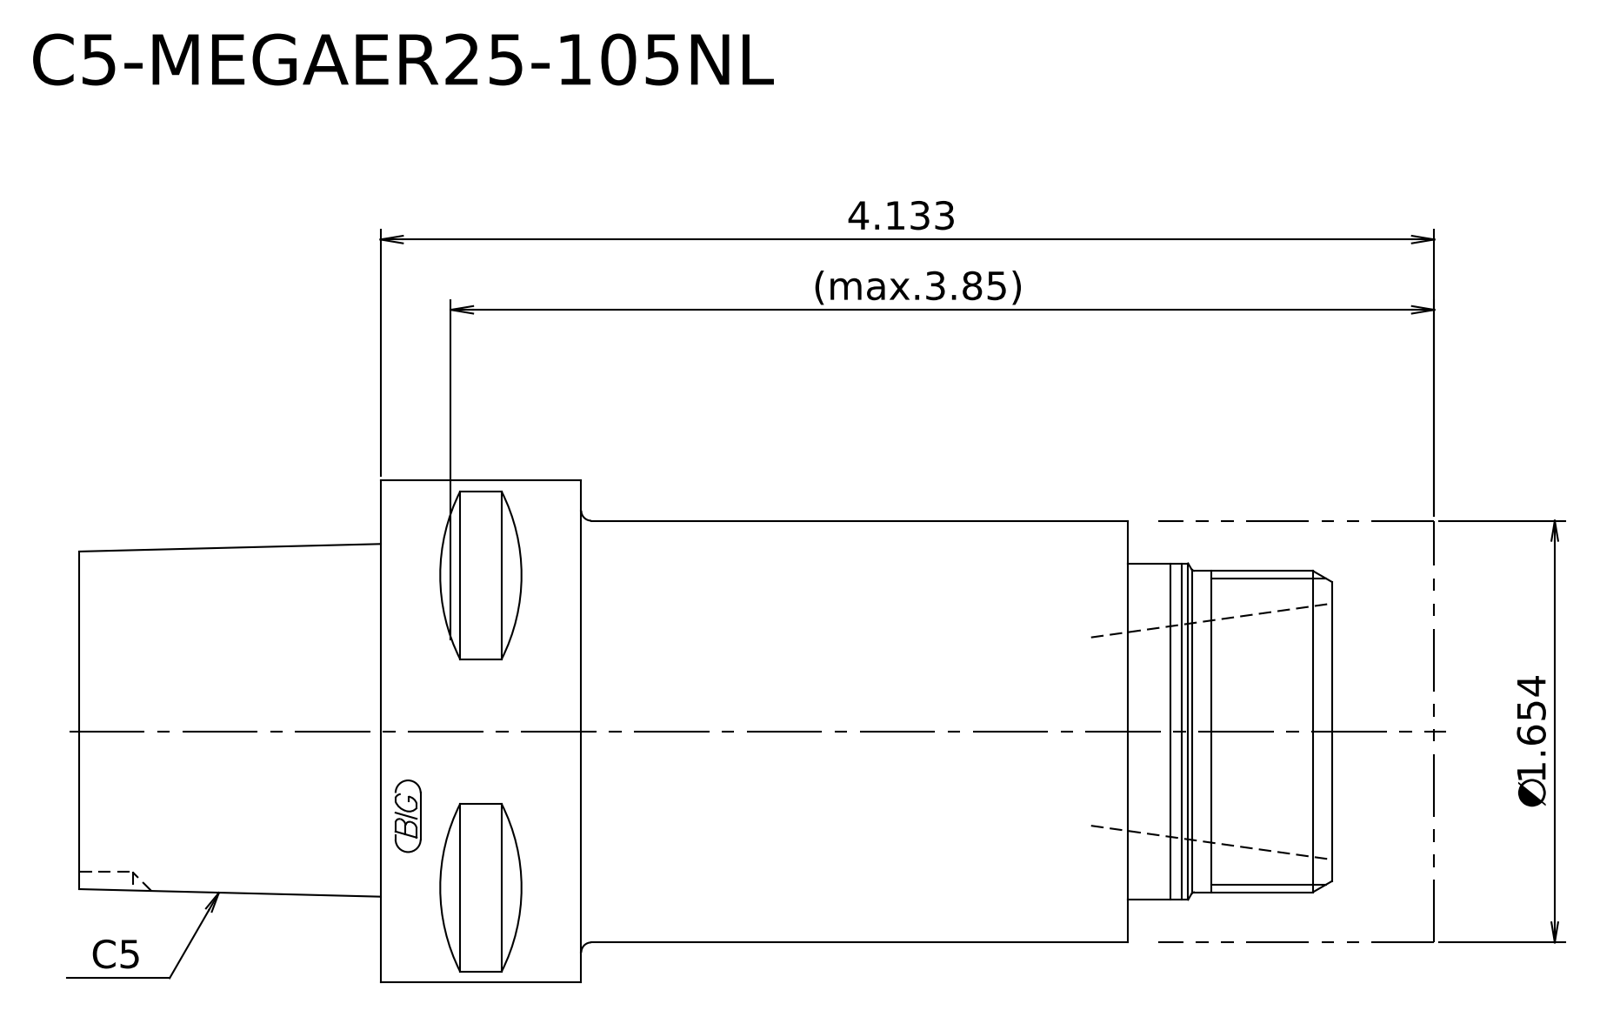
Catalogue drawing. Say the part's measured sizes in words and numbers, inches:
Its 3-D file was written by "Kubotek KeyCreator 2011 V10.0.2 (22737) (automotive_design)". It is 2 solids with 16 faces: 7 planar, 5 cylindrical and 4 other. Overall it measures 5.315 by 1.969 by 1.969 inches. Its volume is 12.01 cubic inches and its surface area 39.83 square inches. Round bosses or shafts: 1 of diameter 1.969, 1 of diameter 1.654, 1 of diameter 1.319, 1 of diameter 1.26. The main face-to-face distances are 1.083, 4.134, 3.051, 5.315, 4.232, 1.181, 0.402, 0.681, 3.732, 4.913.
